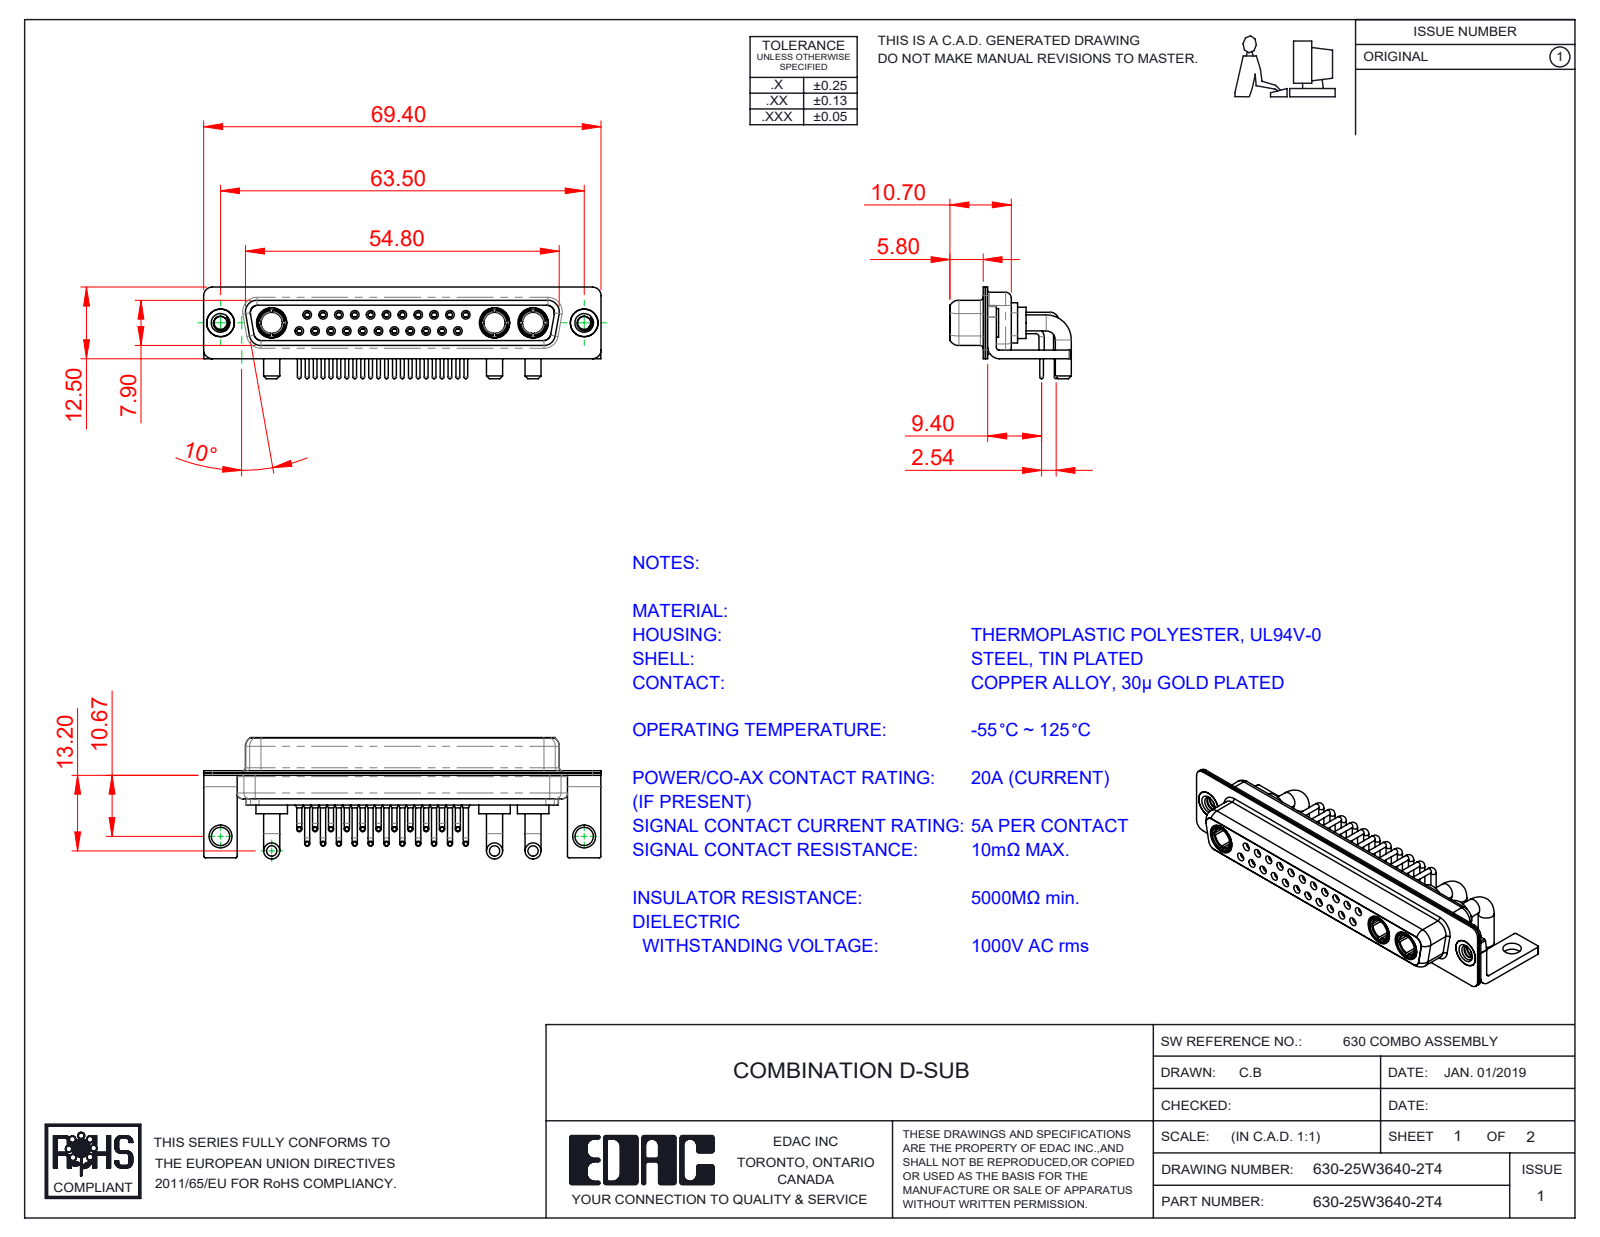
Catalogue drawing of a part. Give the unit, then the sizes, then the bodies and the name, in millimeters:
Units: millimetres
Overall size (bounding box): 69.4 × 21.2 × 16
Round holes (diameter × count): ⌀0.9 ×22, ⌀1.1 ×22, ⌀1.5 ×22, ⌀2 ×22, ⌀1.6 ×11, ⌀1.7 ×11, ⌀4.85 ×5, ⌀3.7 ×3, ⌀5.3 ×3, ⌀2.26 ×2, ⌀3.2 ×2, ⌀4 ×2
Round bosses / shafts (diameter × count): ⌀0.9 ×23, ⌀0.65 ×22, ⌀1.6 ×12, ⌀2.8 ×6, ⌀5.5 ×3, ⌀5.2 ×3, ⌀4.96 ×3, ⌀4.75 ×3
Partial cylindrical surfaces — rounded edges, fillets, slot ends (radius × count): R0.25 ×16, R1.5 ×16, R2 ×13, R1.35 ×8, R1.6 ×8, R0.5 ×5, R0.6 ×4, R0.65 ×4
Main face-to-face distances: 0.4, 0.45, 1.4, 8.45, 1.8, 8.9, 6.2, 7.05, 0.8, 1.35
Hole centre spacings: 3.16, 2.77, 5.54, 5.03, 8.31, 7.48, 11.08, 5.04
Volume: 5 943 mm³ · Surface area: 13 302 mm²
Bodies: 35 solids, 1719 faces (504 planar, 736 cylindrical, 479 other)
Part name (STEP PRODUCT): 630-25W3640-2T4; 630Combo Stabilizer Bracket; 630Combo Shell Rear_37 Contacts; 630Combo Housing_25W3 (+5 more)
STEP written by: SolidWorks 2020 (CONFIG_CONTROL_DESIGN)
